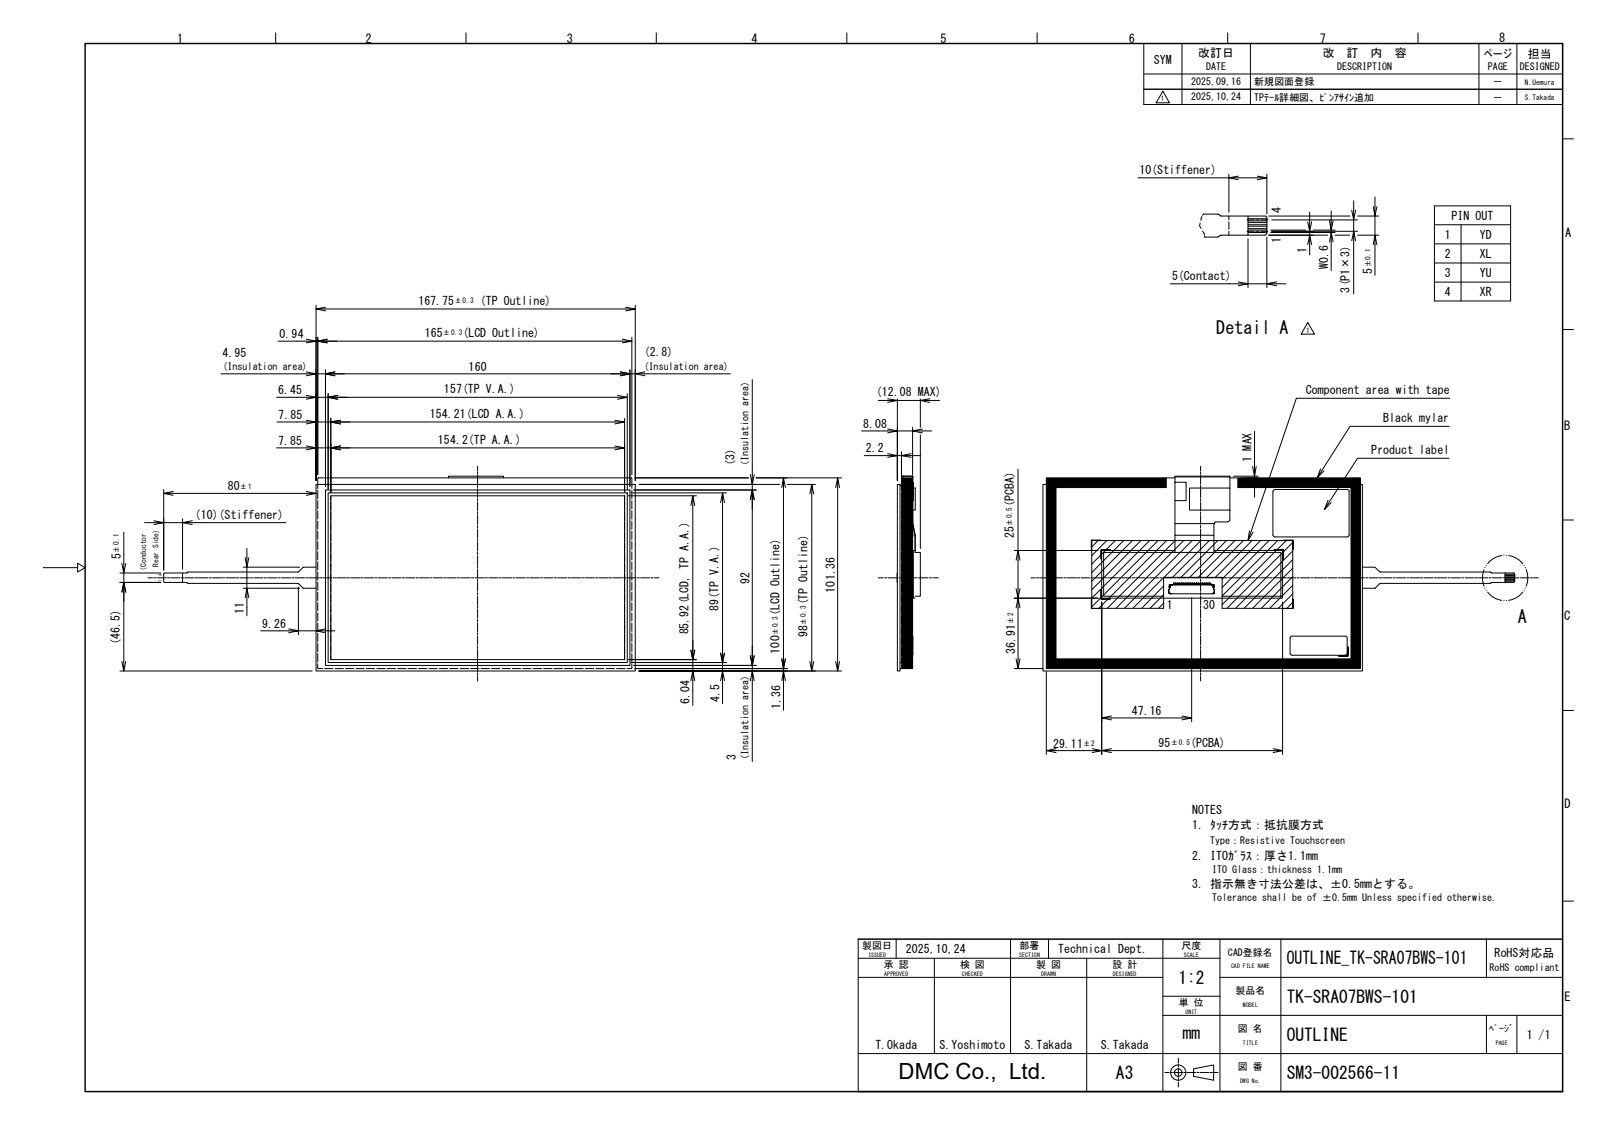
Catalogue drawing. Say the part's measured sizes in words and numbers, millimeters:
The part is named "HP_TK-SRA07BWS-101". Its 3-D file was written by "Autodesk Inventor 2024 (AUTOMOTIVE_DESIGN)". It is 1 solid with 1136 faces: 918 planar, 218 cylindrical and 0 other. Overall it measures 247.75 by 102.36 by 12.19 millimeters. Its volume is 128 949 cubic millimeters and its surface area 73 043 square millimeters. Partial cylindrical surfaces (rounded edges, fillets, slot ends): 95 of radius 0.1, 10 of radius 0.5, 10 of radius 1, 4 of radius 0.33, 2 of radius 0.15, 2 of radius 0.2, 2 of radius 0.3, 2 of radius 0.42. The main face-to-face distances are 1.4, 0.8, 2.2, 8.03, 5.83, 6.63, 5.88, 6.68, 8.08, 4.
